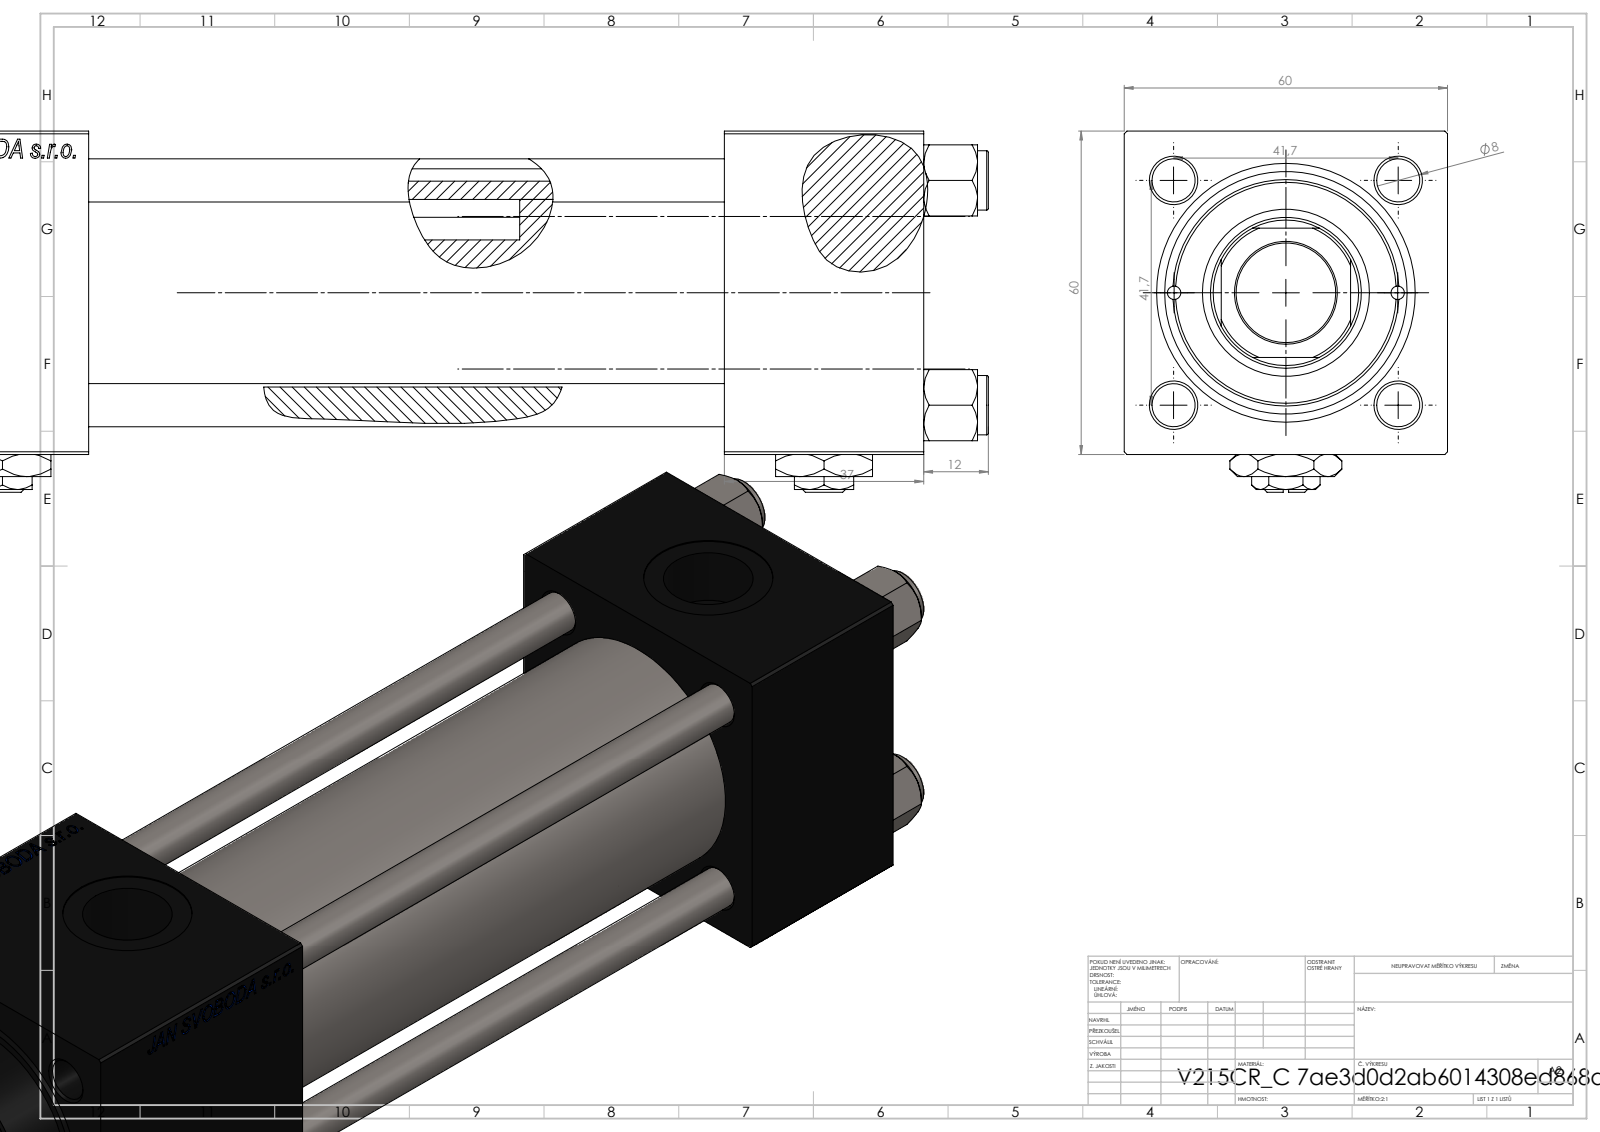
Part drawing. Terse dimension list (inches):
name: NUT_M5_C; Zatka_pro_OIL_PORT; V215_VC_A; V215CR_C_Body (+2 more)
written by: SolidWorks 2019 (CONFIG_CONTROL_DESIGN)
unit: in
bodies: 13 solids, 1256 faces (576 planar, 102 cylindrical, 578 other)
size: 9.646 × 2.638 × 2.362
volume: 30.12 in³; area: 220.2 in²
holes: 4× ⌀0.315, 2× ⌀0.098, 2× ⌀0.276, 2× ⌀0.656, 2× ⌀0.945, 1× ⌀0.728, 1× ⌀1.102, 1× ⌀1.22, 1× ⌀1.575, 1× ⌀1.772
bosses: 4× ⌀0.433, 1× ⌀1.811, 1× ⌀1.654
rounds: 1× R0.531
face distances: 2.362, 1.457, 6.102, 4.646, 2.087, 7.059, 5.602, 0.957, 8.189, 6.732
hole spacings: 0.821, 1.161, 1.642, 1.832, 0.817, 2.322, 1.634, 6.004
